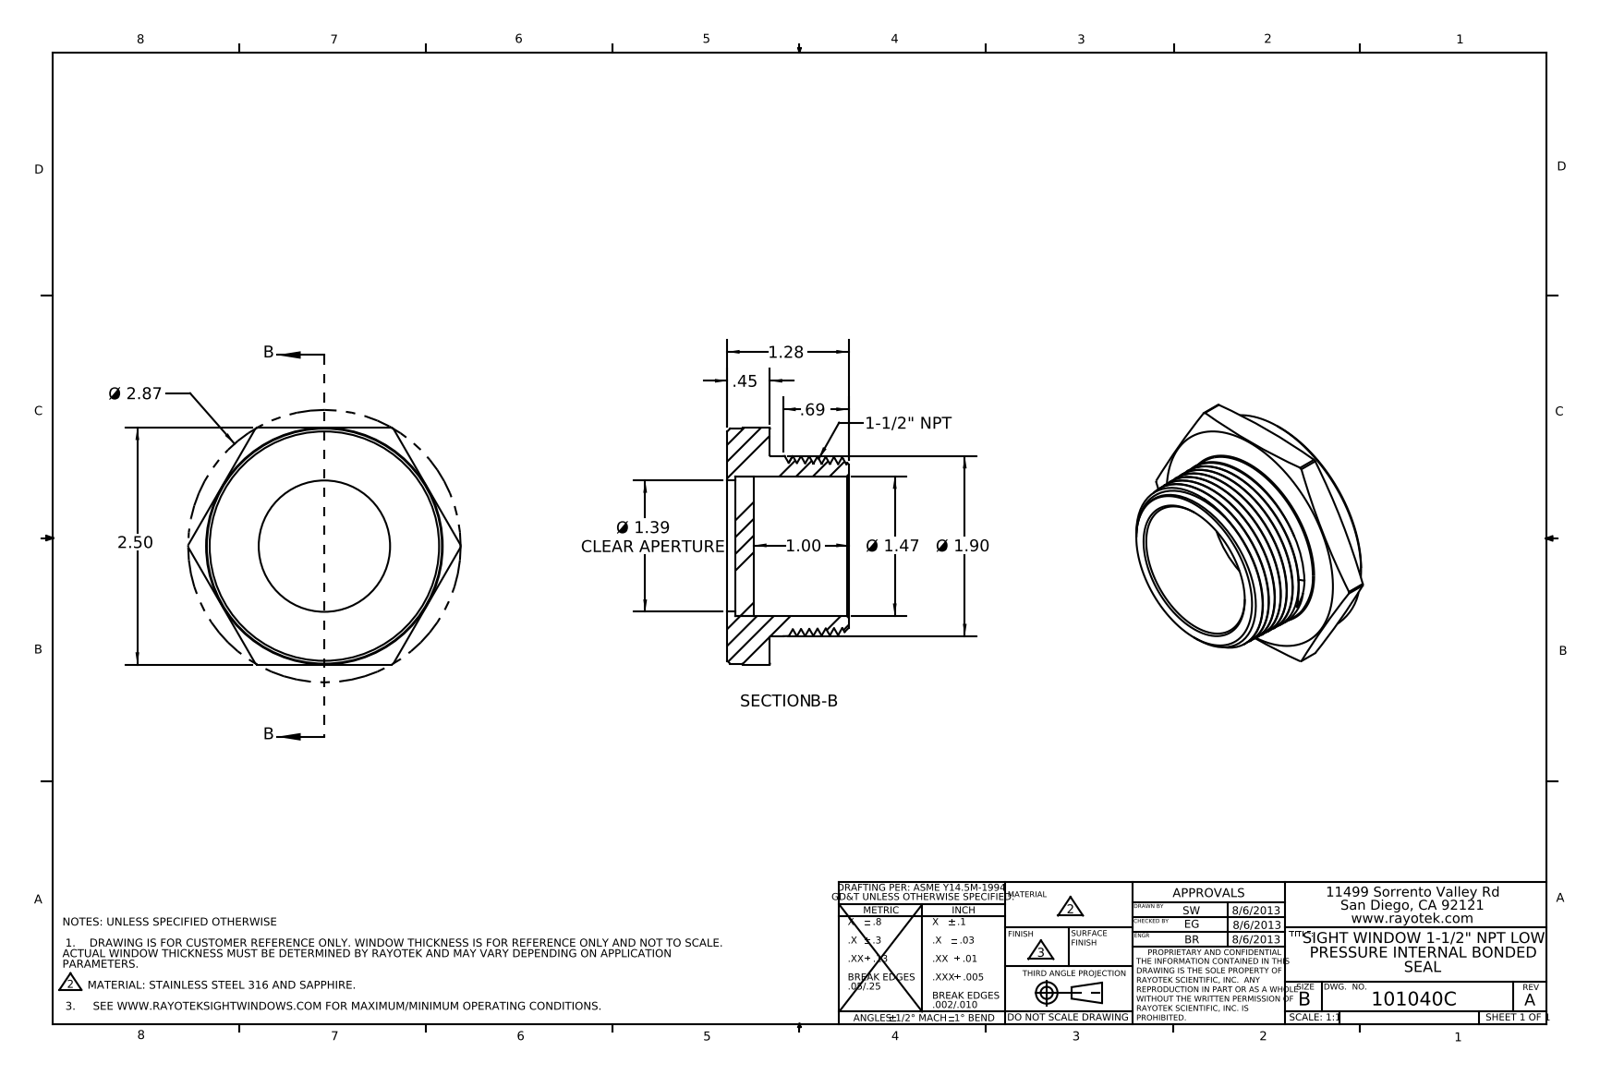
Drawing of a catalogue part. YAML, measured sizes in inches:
part_name: "403040"
step_written_by: "SolidWorks 2012 (AUTOMOTIVE_DESIGN)"
units: inches
bodies: {solids: 2, faces: 65, planar: 15, cylindrical: 17, other: 33}
overall_size: [2.875, 2.5, 1.28]
volume: 2.692
surface_area: 28.84
round_holes:
  - {diameter: 1.386, count: 1}
  - {diameter: 1.47, count: 1}
round_bosses_or_shafts:
  - {diameter: 2.48, count: 1}
  - {diameter: 1.9, count: 1}
partial_cylinders:
  - {radius: 1.437, count: 1}
face_to_face_distances: [0.45, 0.084, 0.366, 0.284, 0.2, 0.166, 2.5, 1.28, 1.196, 0.996]
